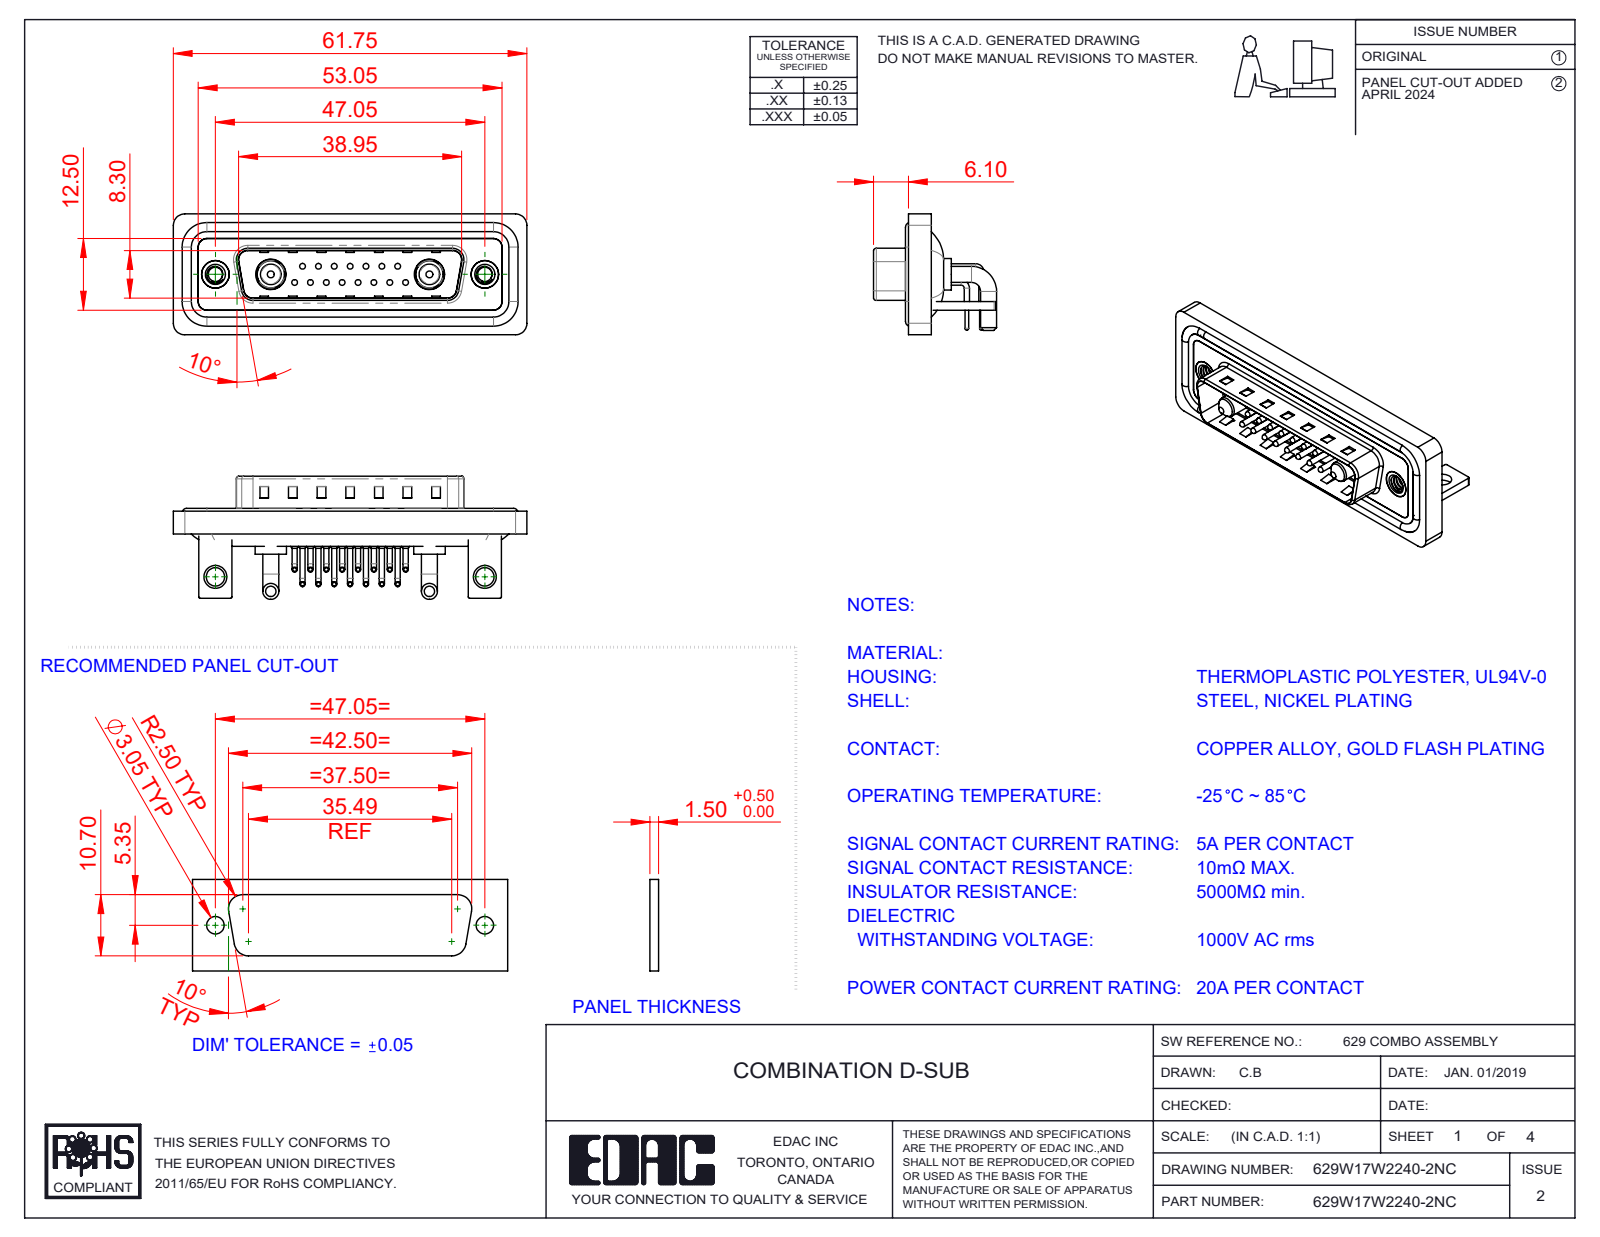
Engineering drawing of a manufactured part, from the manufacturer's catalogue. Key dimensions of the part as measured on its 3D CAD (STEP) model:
Part name (STEP PRODUCT): 629Combo Contact Row 2; 629Combo Waterproof Housing_25 Contacts; 629Combo Shell Rear_25 Contacts; 629Combo Shell Front_25 Contacts (+6 more)
STEP written by: SolidWorks 2023 (CONFIG_CONTROL_DESIGN)
Units: millimetres
Bodies: 28 solids, 2257 faces (1209 planar, 788 cylindrical, 260 other)
Overall size (bounding box): 61.75 × 21.5 × 21.1
Volume: 7 784 mm³ · Surface area: 13 189 mm²
Round holes (diameter × count): ⌀0.75 ×15, ⌀1.6 ×15, ⌀2 ×15, ⌀2.5 ×2, ⌀3.2 ×2, ⌀4 ×2, ⌀4.8 ×2, ⌀4.85 ×2, ⌀5 ×2, ⌀5.3 ×2
Round bosses / shafts (diameter × count): ⌀0.9 ×30, ⌀1.5 ×15, ⌀1 ×15, ⌀0.65 ×15, ⌀2.8 ×4, ⌀1.6 ×4, ⌀5.5 ×2, ⌀5.2 ×2
Partial cylindrical surfaces — rounded edges, fillets, slot ends (radius × count): R2 ×19, R1.5 ×18, R0.25 ×16, R1.01 ×15, R0.5 ×9, R1.6 ×8, R0.6 ×4, R0.65 ×4
Main face-to-face distances: 0.4, 0.8, 1.5, 2.1, 2.9, 1.1, 4.1, 1.6, 4.5, 3.7
Hole centre spacings: 3.16, 2.77, 5.54, 8.31, 5.04, 7.49, 11.08, 5.03
